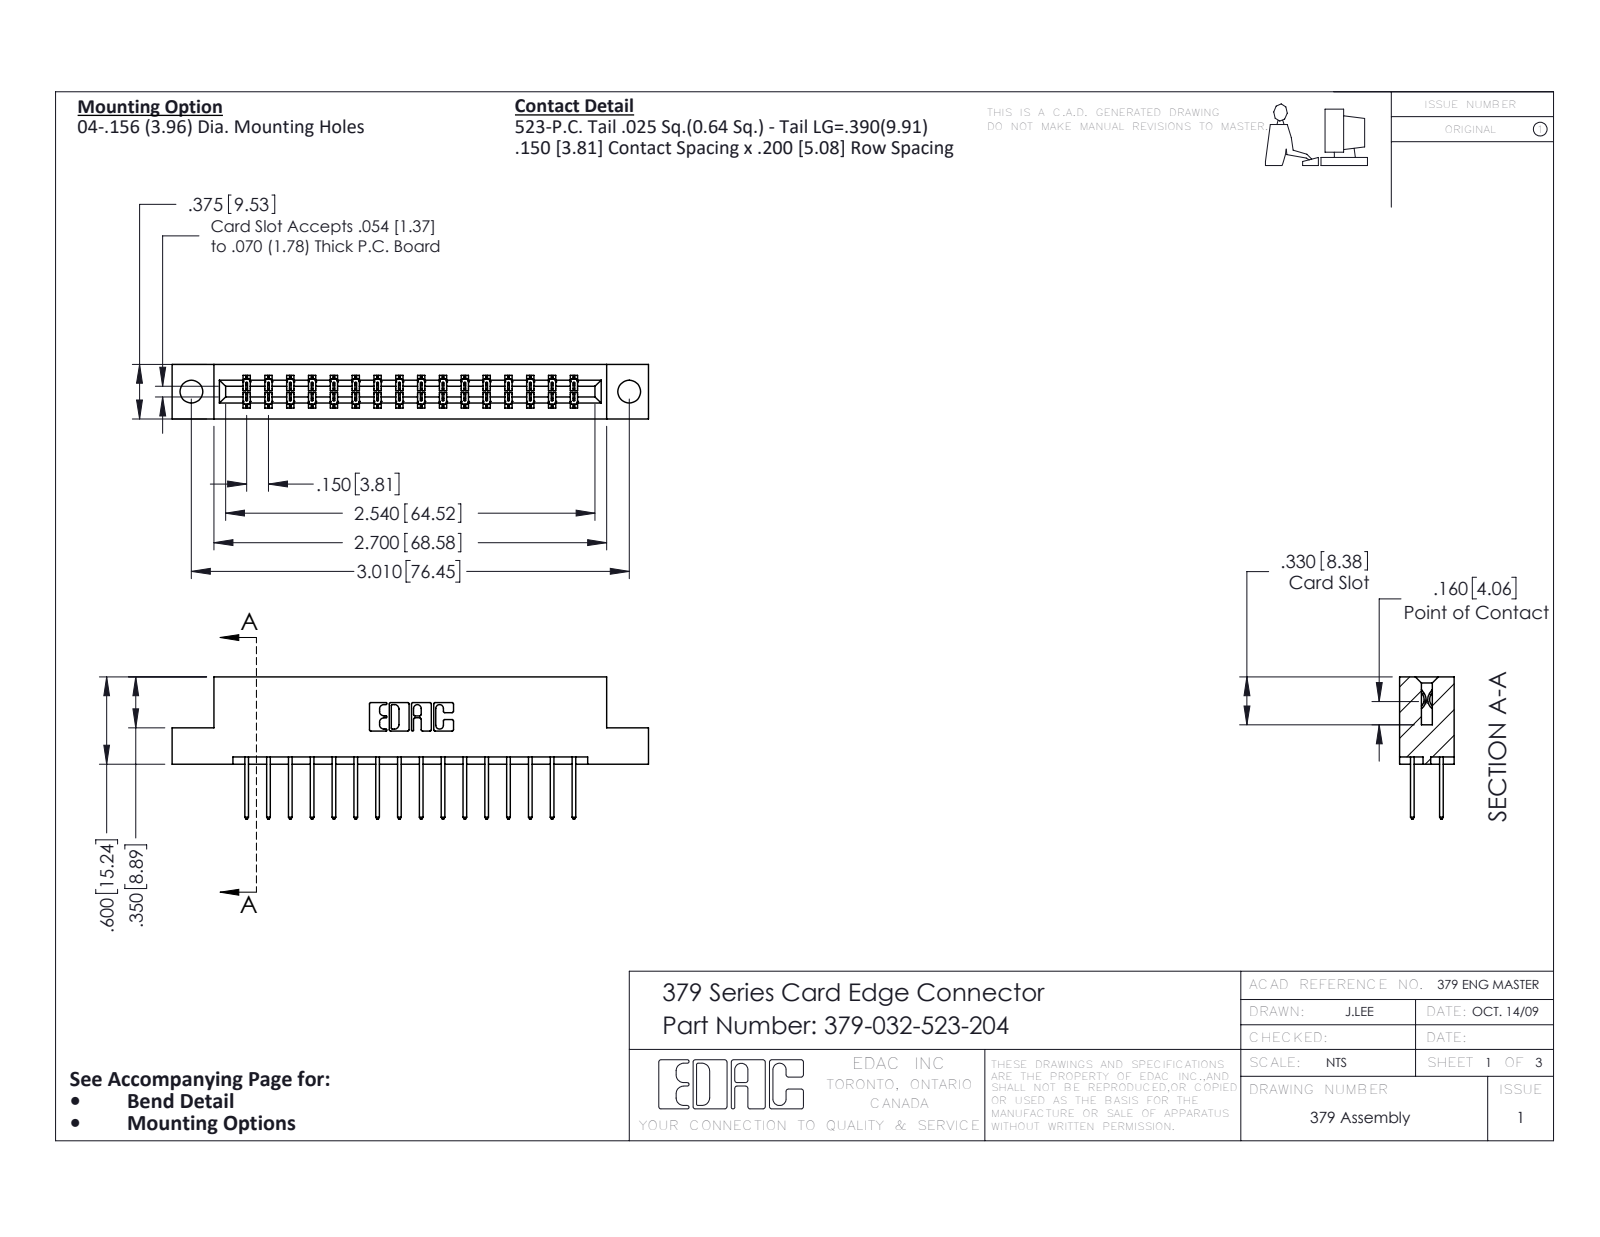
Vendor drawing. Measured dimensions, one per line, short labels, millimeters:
name: 345-292-001_345-293-123; 379 Part_Flush - .156 Dia - TH; 379-032-523-204
written by: SolidWorks 2020 (CONFIG_CONTROL_DESIGN)
unit: mm
bodies: 33 solids, 1778 faces (1222 planar, 556 cylindrical, 0 other)
size: 83.2 × 24.8 × 9.5
volume: 8 500 mm³; area: 9 432 mm²
holes: 2× ⌀4
rounds: 63× R0.2, 32× R0.3, 22× R0.3, 6× R0.2, 6× R0.8, 3× R0.7, 2× R0.4, 2× R0.6
face distances: 7.6, 1.9, 5.1, 9.5, 2.5, 3.8, 1.3, 15.2, 5.7, 7
hole spacings: 76.5
